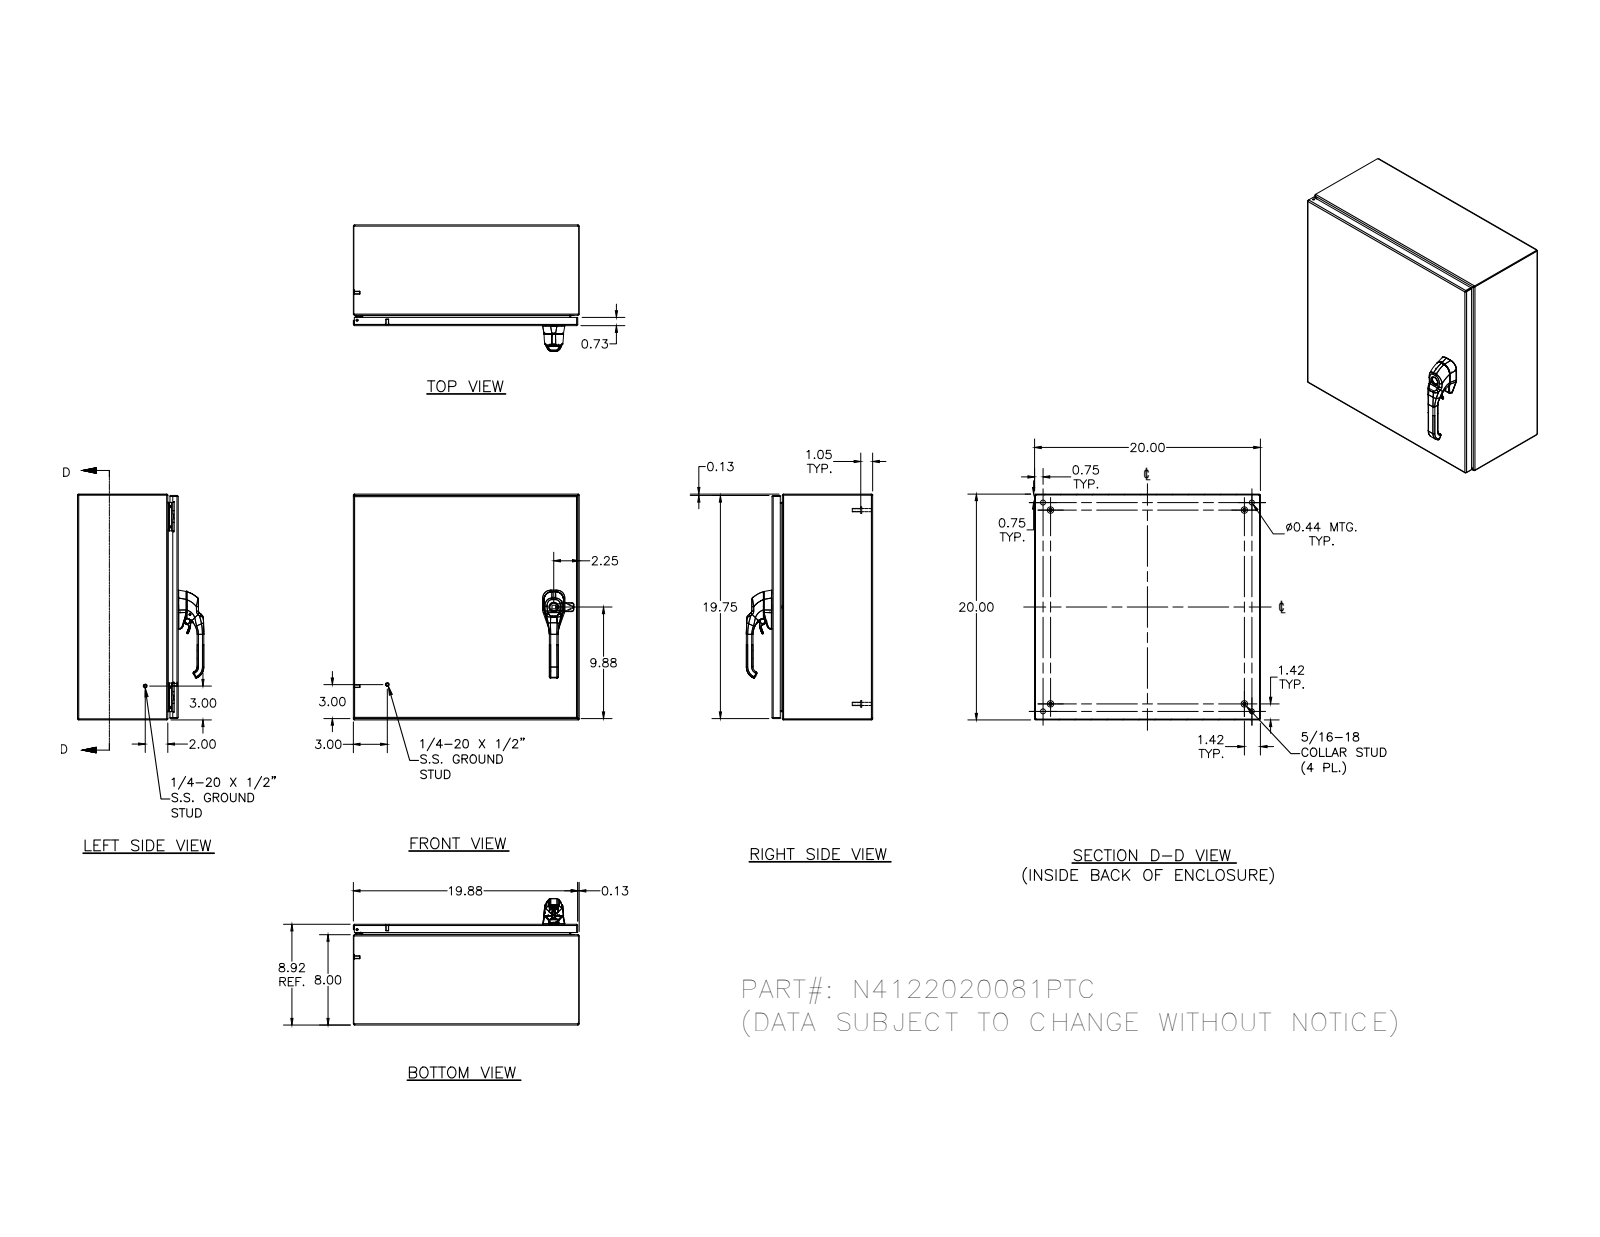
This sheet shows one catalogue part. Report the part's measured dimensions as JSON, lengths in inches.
{"part_name": "N4122020081PTC", "step_written_by": "SolidWorks 2018 (AUTOMOTIVE_DESIGN)", "units": "inches", "bodies": {"solids": 28, "faces": 1280, "planar": 417, "cylindrical": 474, "other": 389}, "overall_size": [20, 20, 11.095], "volume_in3": 128, "surface_area_in2": 3255, "round_holes": [[0.188, 5], [0.093, 4], [0.152, 4], [0.167, 4], [0.172, 4], [0.437, 4], [0.28, 3], [0.156, 2], [0.187, 1]], "round_bosses_or_shafts": [[0.25, 10], [0.563, 4], [0.36, 4], [0.32, 4], [0.3, 4], [0.275, 4], [0.256, 4], [0.164, 4]], "partial_cylinders_radius": [[0.031, 30], [0.05, 26], [0.105, 20], [0.016, 18], [0.125, 14], [0.032, 8], [0.067, 8], [0.068, 8]], "face_to_face_distances": [0.074, 8.843, 19.926, 8.917, 8.769, 20, 19.852, 7.926, 0.917, 0.739], "hole_center_spacings": [15.996, 18.5, 18.872, 0.017, 0.66, 16.004, 16.656, 0.019]}
